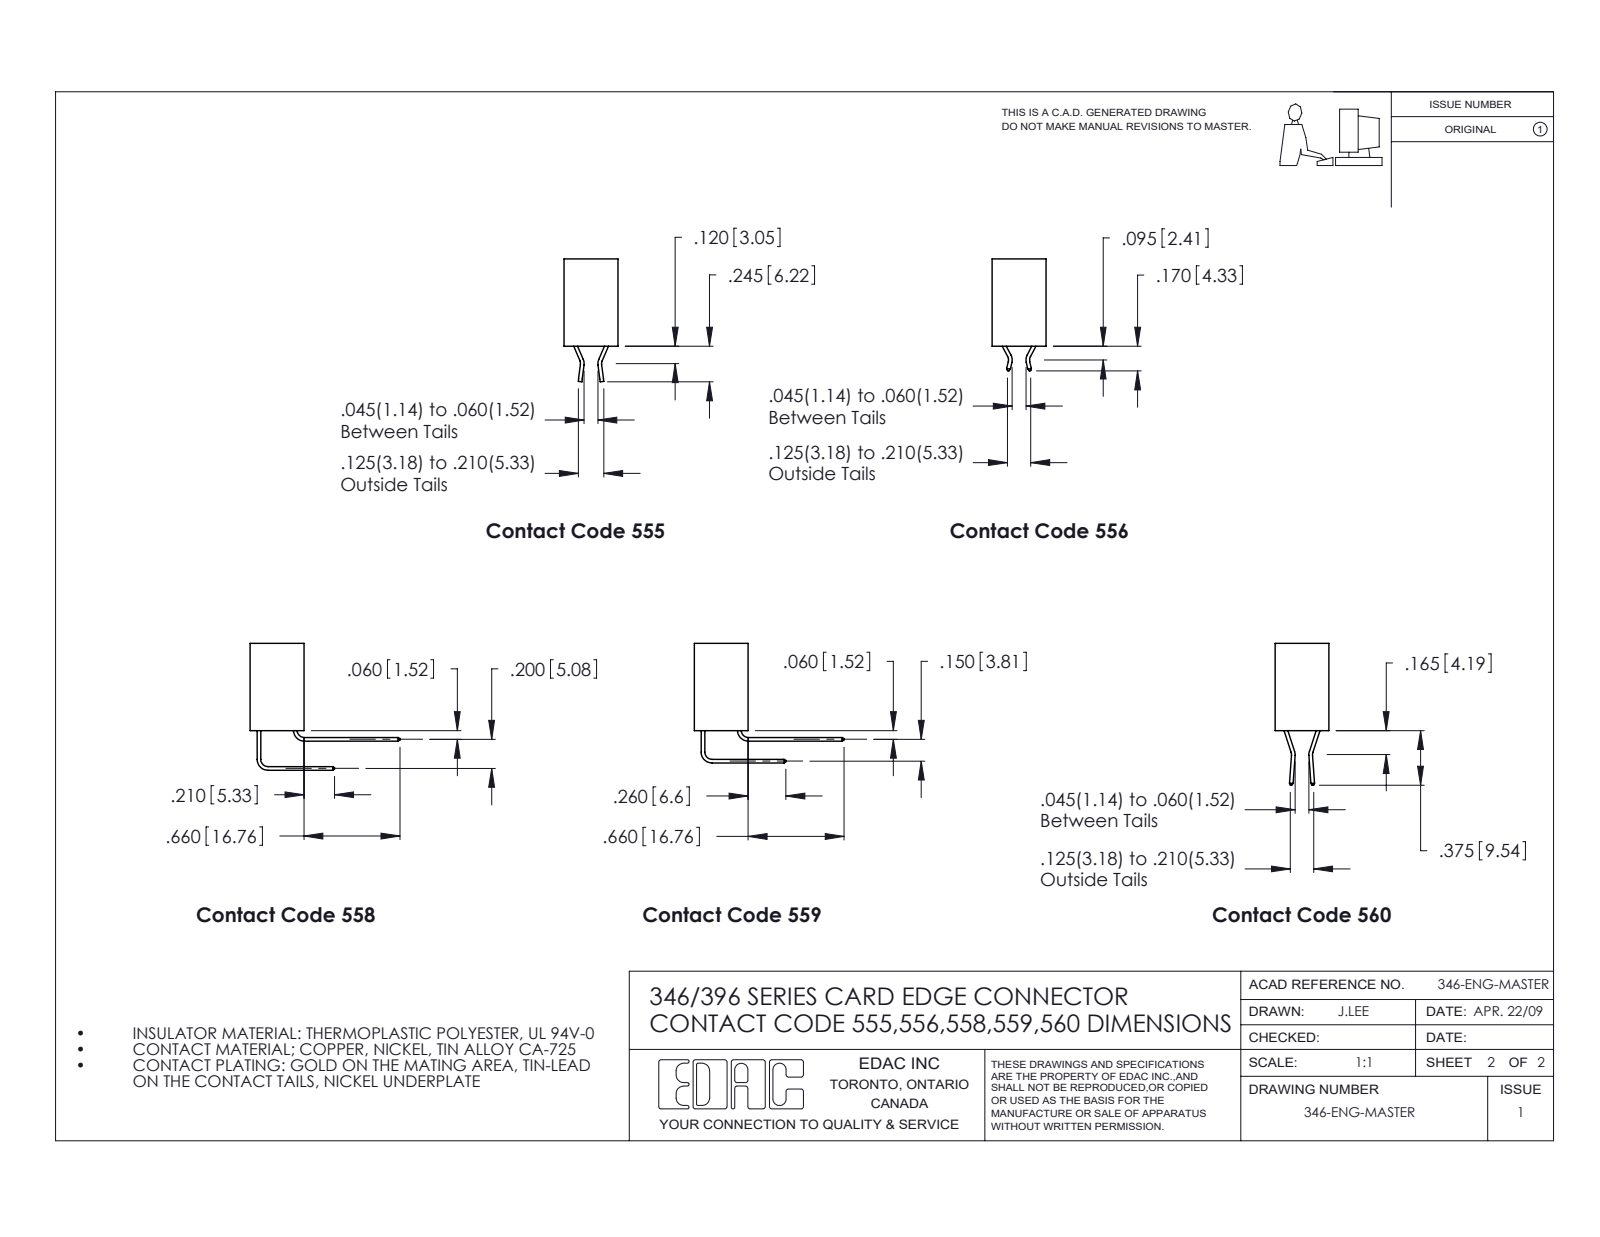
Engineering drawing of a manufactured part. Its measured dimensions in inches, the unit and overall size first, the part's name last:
Units: inches
Overall size (bounding box): 1.03 × 0.91 × 0.673
Round holes (diameter × count): ⌀0.064 ×1
Partial cylindrical surfaces — rounded edges, fillets, slot ends (radius × count): R0.01 ×22, R0.006 ×10, R0.007 ×6, R0.031 ×6, R0.026 ×3, R0.031 ×2, R0.04 ×2, R0.014 ×1
Main face-to-face distances: 0.25, 0.048, 0.37, 0.322, 0.025, 0.072, 0.148, 0.222, 0.1, 0.174
Volume: 0.154 in³ · Surface area: 4.541 in²
Bodies: 6 solids, 414 faces (282 planar, 132 cylindrical, 0 other)
Part name (STEP PRODUCT): 345-292-001_558 559 Tail - 1; 346 Part_No Mounting Lugs; 396-005-559-101
STEP written by: SolidWorks 2020 (CONFIG_CONTROL_DESIGN)
